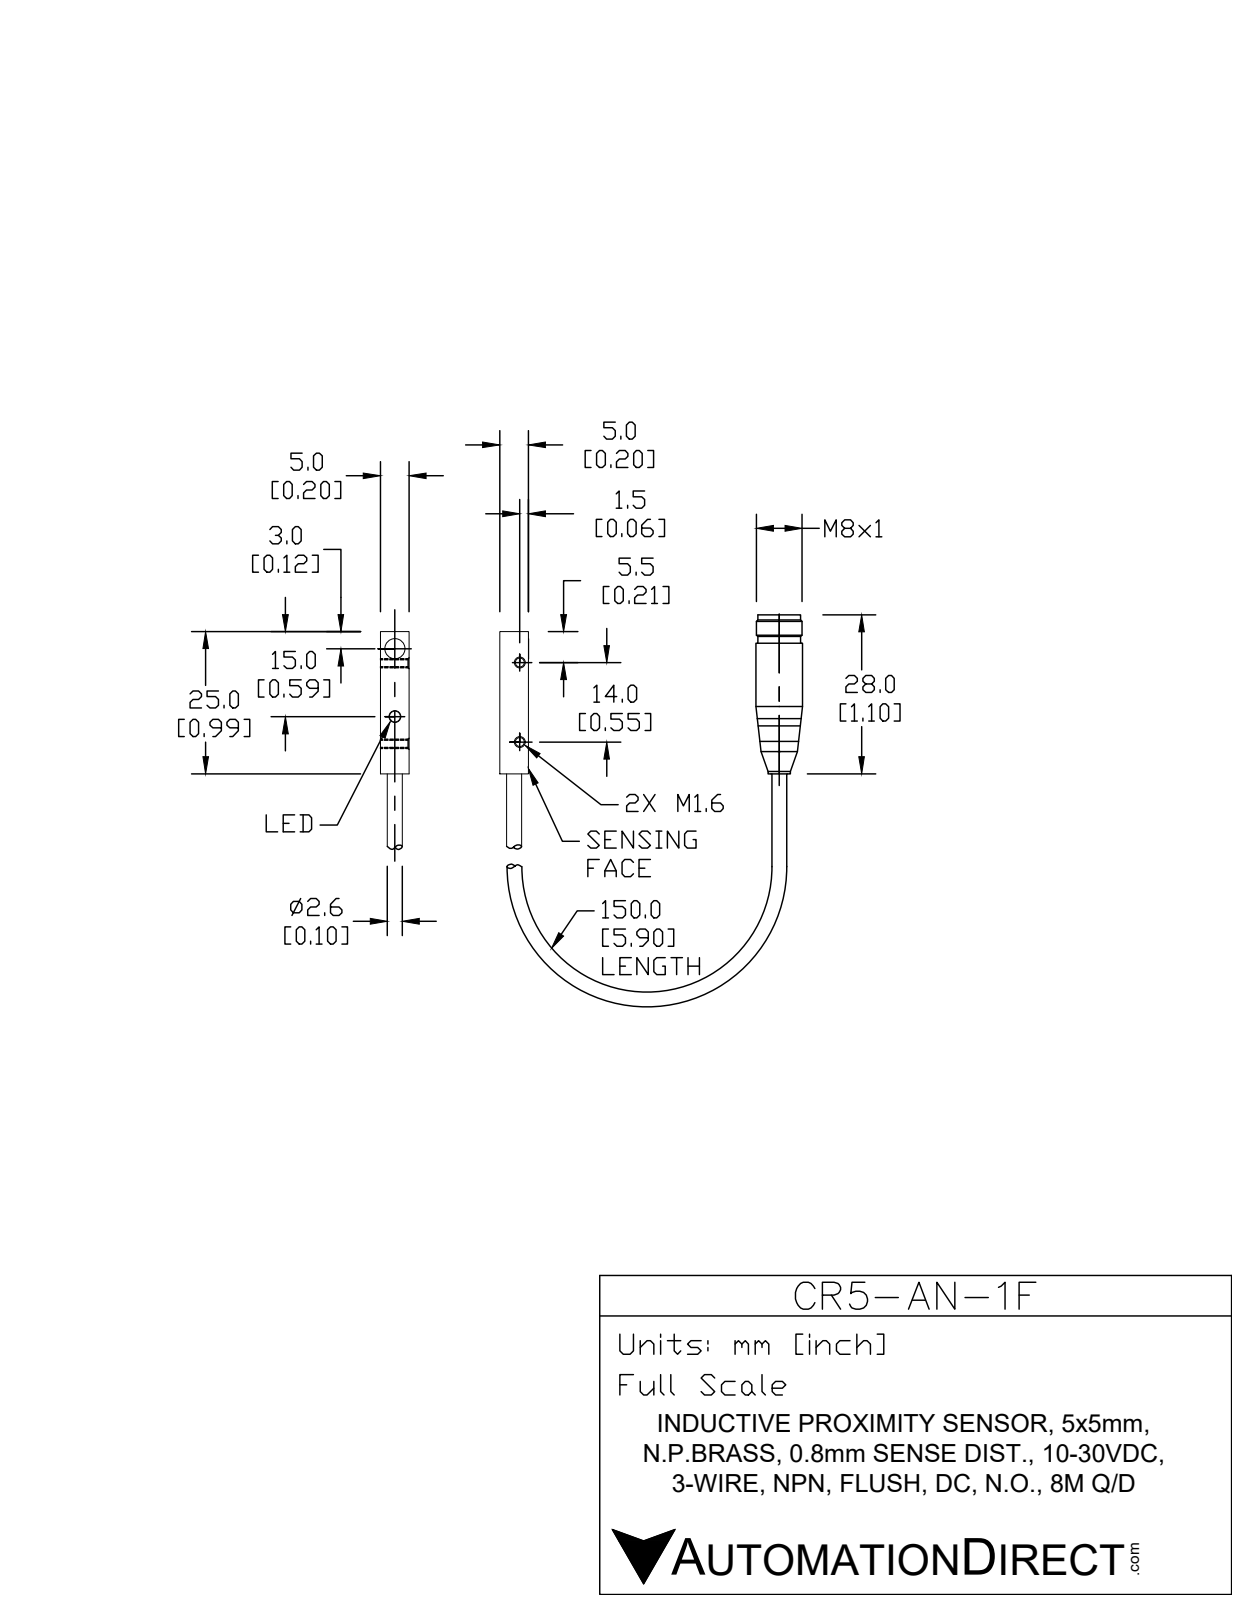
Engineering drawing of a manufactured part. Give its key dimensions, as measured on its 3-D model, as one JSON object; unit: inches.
{"part_name": "CR5-AN-1F", "step_written_by": "SolidWorks 2017 (AUTOMOTIVE_DESIGN)", "units": "inches", "bodies": {"solids": 2, "faces": 359, "planar": 127, "cylindrical": 84, "other": 148}, "overall_size": [3.732, 0.393, 0.393], "volume_in3": 0.158, "surface_area_in2": 3.343, "round_holes": [[0.049, 2], [0.228, 1]], "round_bosses_or_shafts": [[0.039, 3], [0.386, 1], [0.315, 1], [0.295, 1], [0.272, 1], [0.256, 1], [0.102, 1]], "partial_cylinders_radius": [[0.008, 8], [0.197, 1]], "face_to_face_distances": [0.197, 0.035, 0.071, 0.106, 2.362, 0.256, 1.173, 3.535, 2.551, 1.378], "hole_center_spacings": [0.551]}
